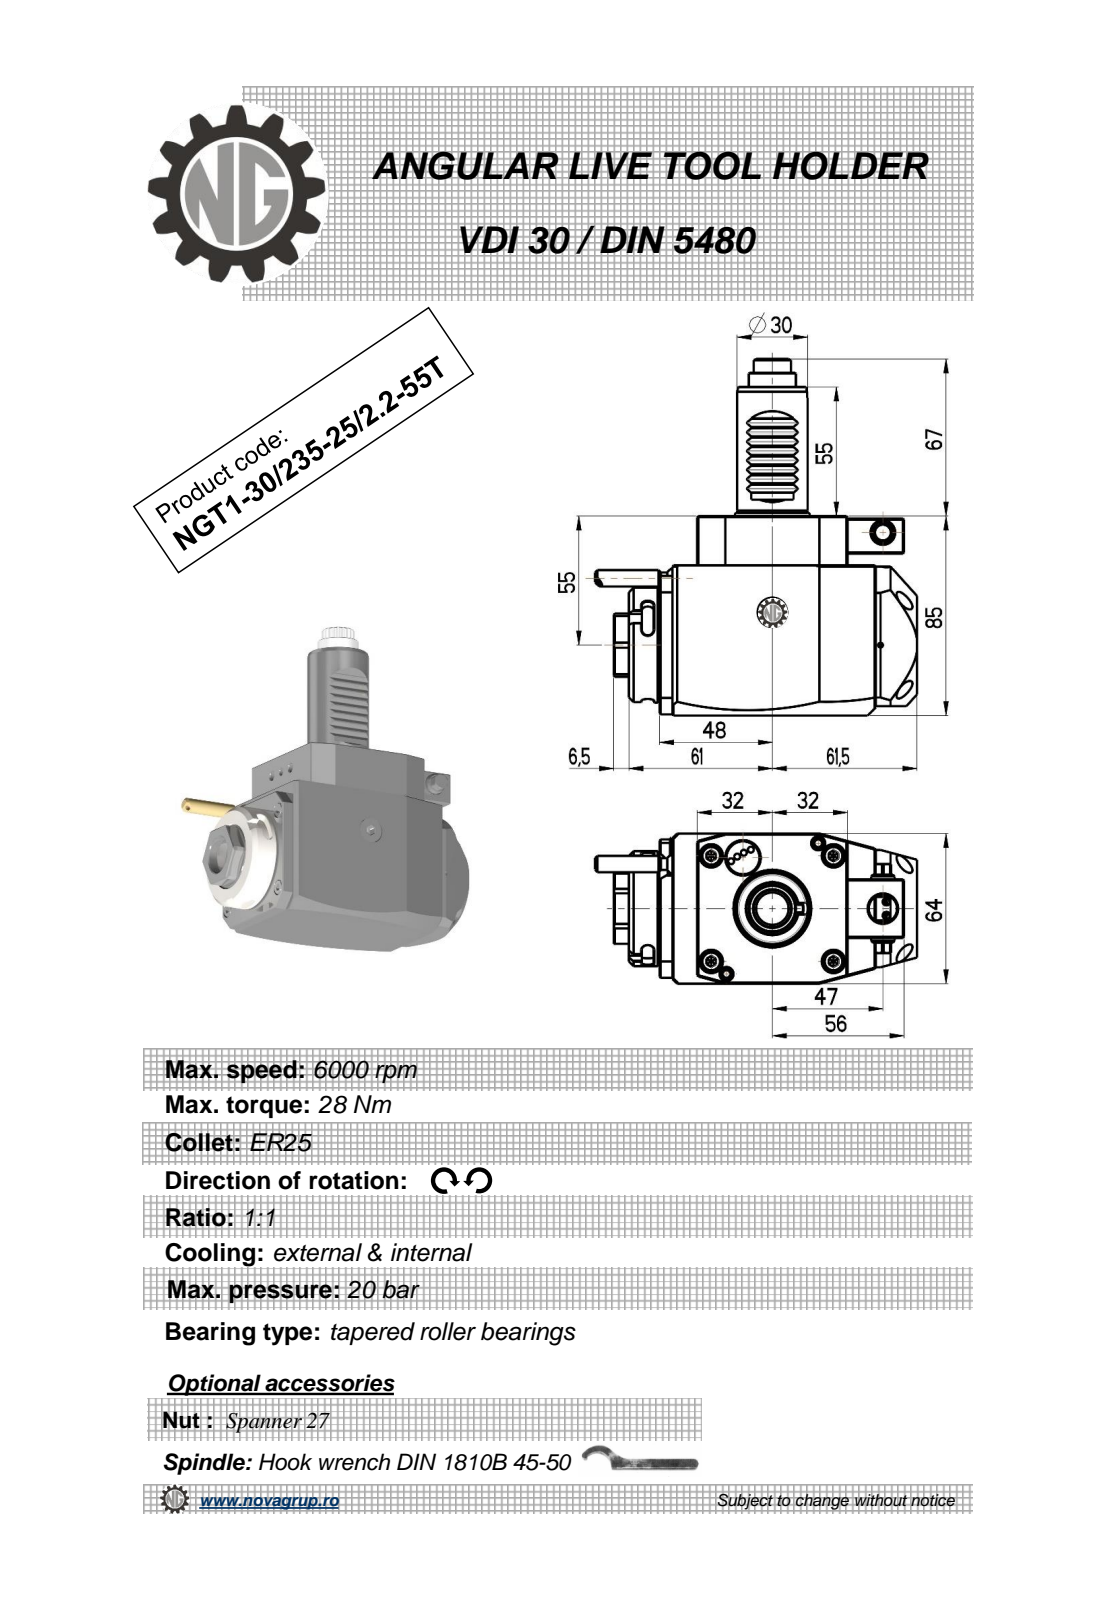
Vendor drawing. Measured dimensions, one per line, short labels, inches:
name: NGT1_30_235_25_1_2_55T
written by: PRO/ENGINEER BY PARAMETRIC TECHNOLOGY CORPORATION, 2010280 (CONFIG_CONTROL_DESIGN)
unit: in
bodies: 1 solid, 427 faces (186 planar, 153 cylindrical, 88 other)
size: 5.984 × 5.389 × 2.52
volume: 34.12 in³; area: 79.11 in²
holes: 1× ⌀0.098, 1× ⌀0.118, 1× ⌀0.374, 1× ⌀0.472, 1× ⌀0.709
bosses: 2× ⌀0.315, 1× ⌀1.929, 1× ⌀1.654, 1× ⌀1.181, 1× ⌀0.787, 1× ⌀0.394, 1× ⌀0.276, 1× ⌀0.197
rounds: 36× R0.078, 8× R0.012, 6× R0.098, 2× R7.087, 1× R0.152, 1× R0.167, 1× R0.177, 1× R0.279
face distances: 2.52, 3.346, 0.63, 0.512, 4.311, 0.827, 3.15, 4.823, 1.142, 3.681
hole spacings: 1.03, 1.348, 1.831
